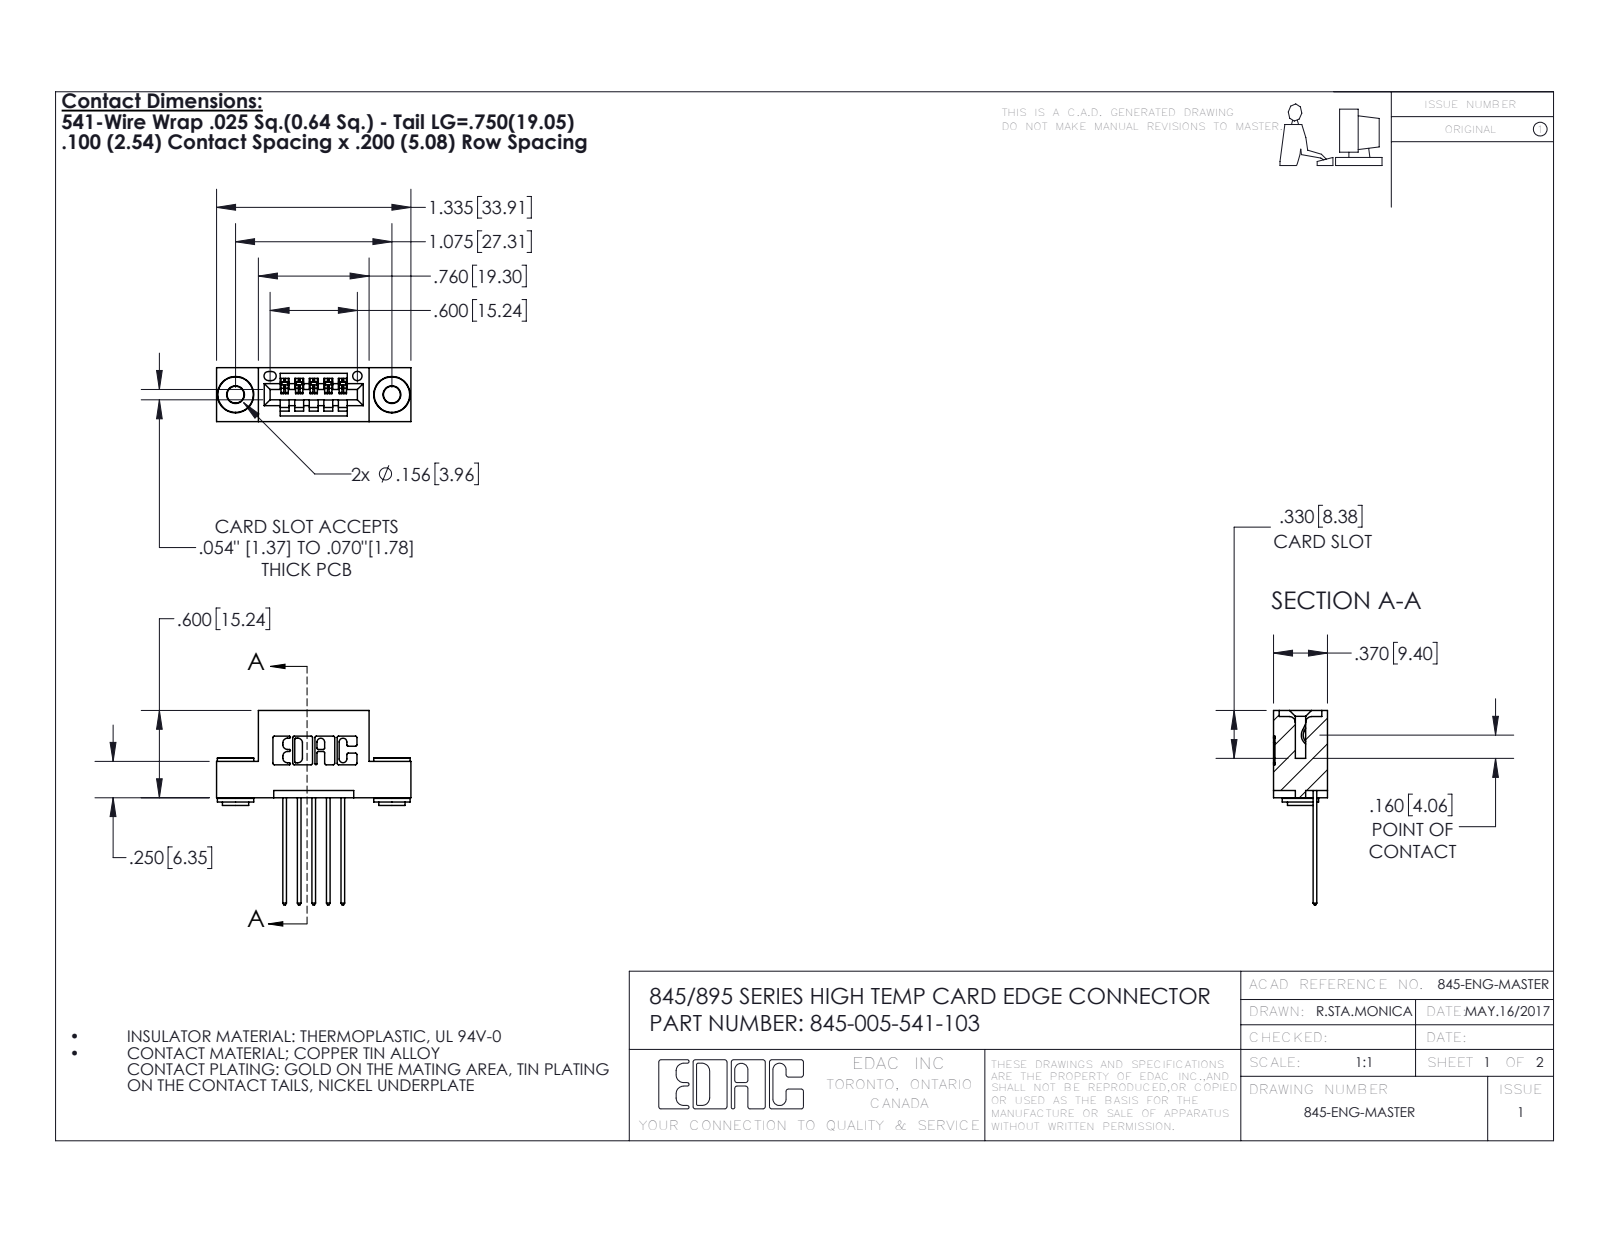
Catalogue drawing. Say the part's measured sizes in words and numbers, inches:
The part is named "345-250-002_345-250-002-102; 345-292-001_345-293-141; 345 Part_Flush Mounting Lugs - 0.156 Dia-TH; 345-005-541-103". Its 3-D file was written by "SolidWorks 2016 (CONFIG_CONTROL_DESIGN)". It is 8 solids with 454 faces: 290 planar, 156 cylindrical and 8 other. Overall it measures 1.337 by 1.335 by 0.37 inches. Its volume is 0.18 cubic inches and its surface area 5.787 square inches. Round holes: 2 of diameter 0.116, 2 of diameter 0.156, 1 of diameter 0.064. Round bosses or shafts: 2 of diameter 0.25, 2 of diameter 0.18, 2 of diameter 0.136. Partial cylindrical surfaces (rounded edges, fillets, slot ends): 22 of radius 0.01, 10 of radius 0.006, 10 of radius 0.01, 6 of radius 0.007, 6 of radius 0.031, 3 of radius 0.026, 2 of radius 0.031, 2 of radius 0.04. The main face-to-face distances are 0.2, 0.37, 0.072, 0.298, 0.1, 0.025, 0.25, 0.098, 0.272, 0.3. The hole center spacings are 0.27, 0.847, 1.075.
